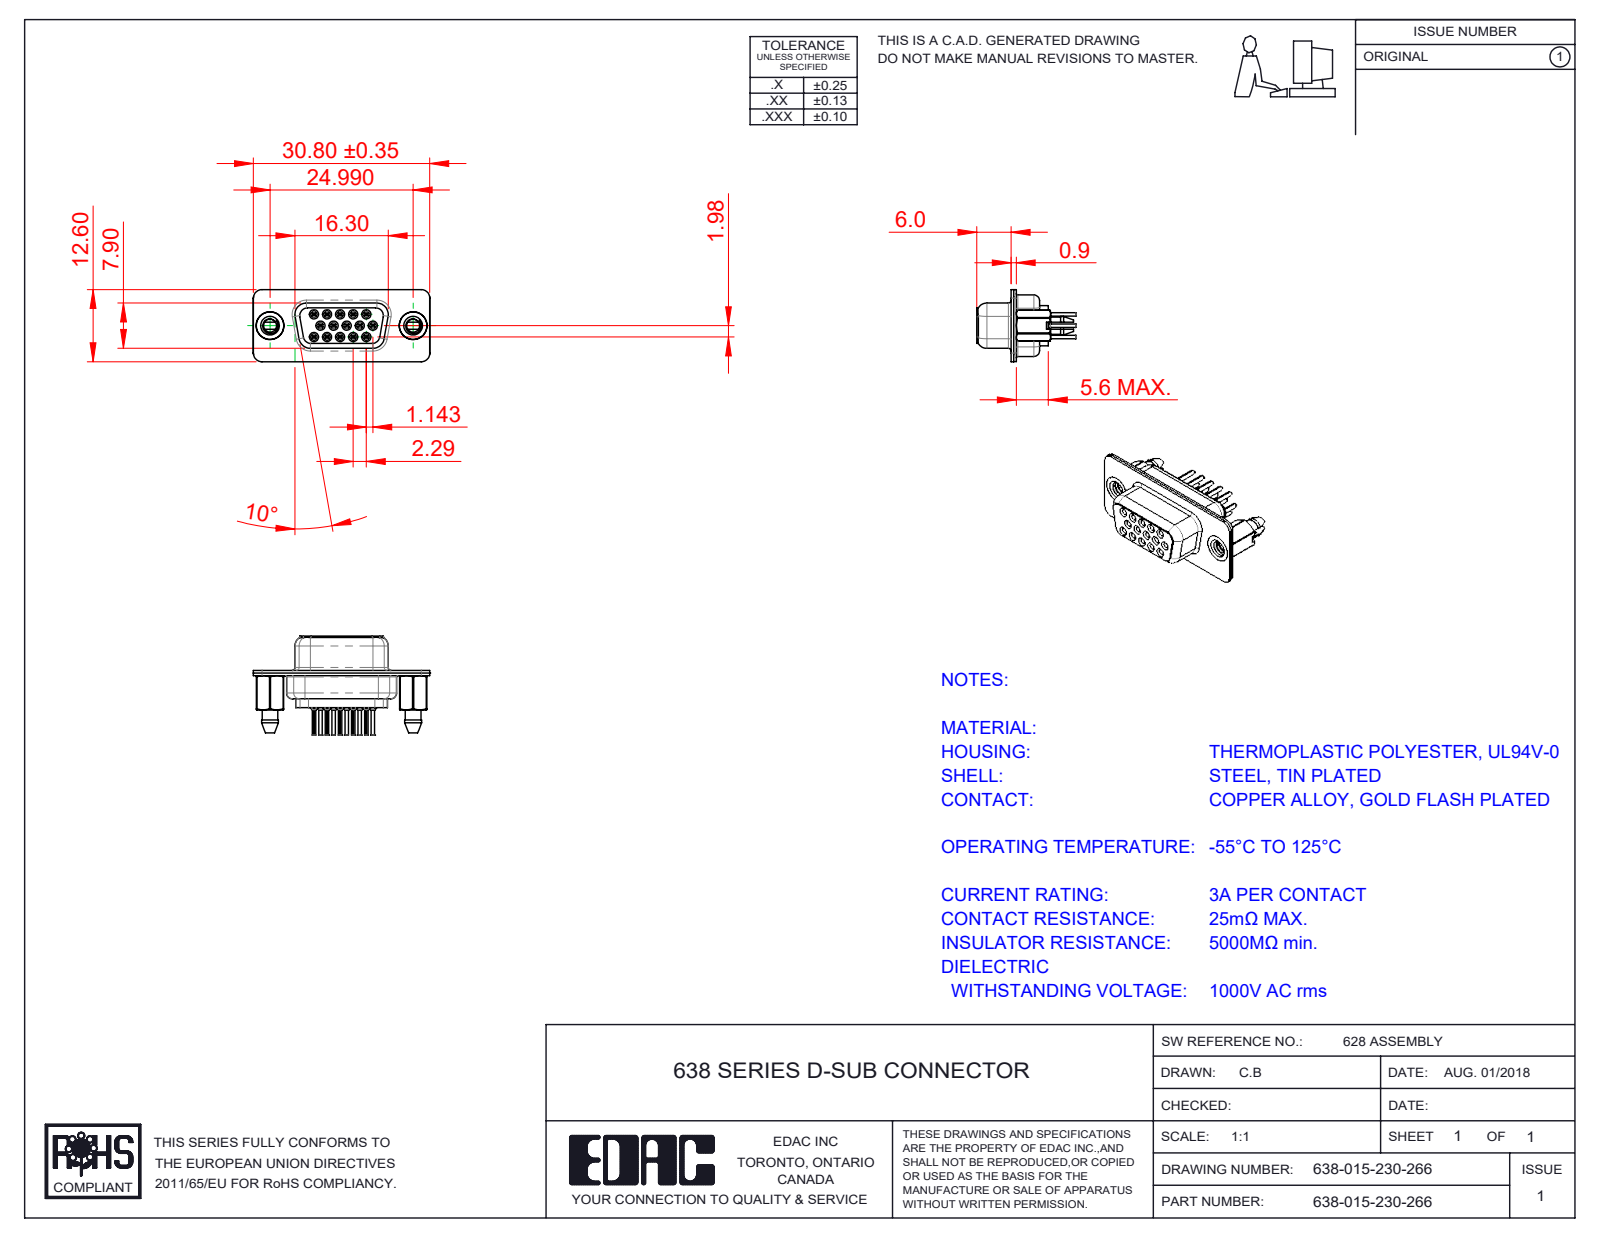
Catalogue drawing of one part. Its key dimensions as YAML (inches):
part_name: "638 Contact Row 1_30; 638 Shell Rear_15 Contacts; 638 Contact Row 3_30; 638-015-230-266 (+4 more)"
step_written_by: "SolidWorks 2020 (CONFIG_CONTROL_DESIGN)"
units: inches
bodies: {solids: 20, faces: 2258, planar: 564, cylindrical: 664, other: 1030}
overall_size: [1.213, 0.681, 0.496]
volume: 0.103
surface_area: 9.12
round_holes:
  - {diameter: 0.008, count: 15}
  - {diameter: 0.031, count: 15}
  - {diameter: 0.039, count: 15}
  - {diameter: 0.043, count: 15}
  - {diameter: 0.063, count: 15}
  - {diameter: 0.067, count: 15}
  - {diameter: 0.071, count: 15}
  - {diameter: 0.079, count: 2}
  - {diameter: 0.089, count: 2}
  - {diameter: 0.157, count: 2}
  - {diameter: 0.159, count: 2}
  - {diameter: 0.191, count: 2}
round_bosses_or_shafts:
  - {diameter: 0.079, count: 15}
  - {diameter: 0.059, count: 15}
  - {diameter: 0.047, count: 15}
  - {diameter: 0.024, count: 15}
  - {diameter: 0.195, count: 2}
  - {diameter: 0.189, count: 2}
partial_cylinders:
  - {radius: 0.004, count: 30}
  - {radius: 0.059, count: 22}
  - {radius: 0.079, count: 12}
  - {radius: 0.011, count: 10}
  - {radius: 0.061, count: 8}
  - {radius: 0.053, count: 5}
  - {radius: 0.01, count: 4}
  - {radius: 0.02, count: 4}
face_to_face_distances: [0.018, 0.035, 0.016, 0.056, 0.35, 0.26, 0.055, 0.09, 0.236, 0.187]
hole_center_spacings: [0.156, 0.09, 0.18, 0.09, 0.238, 0.238, 0.27, 0.312]
